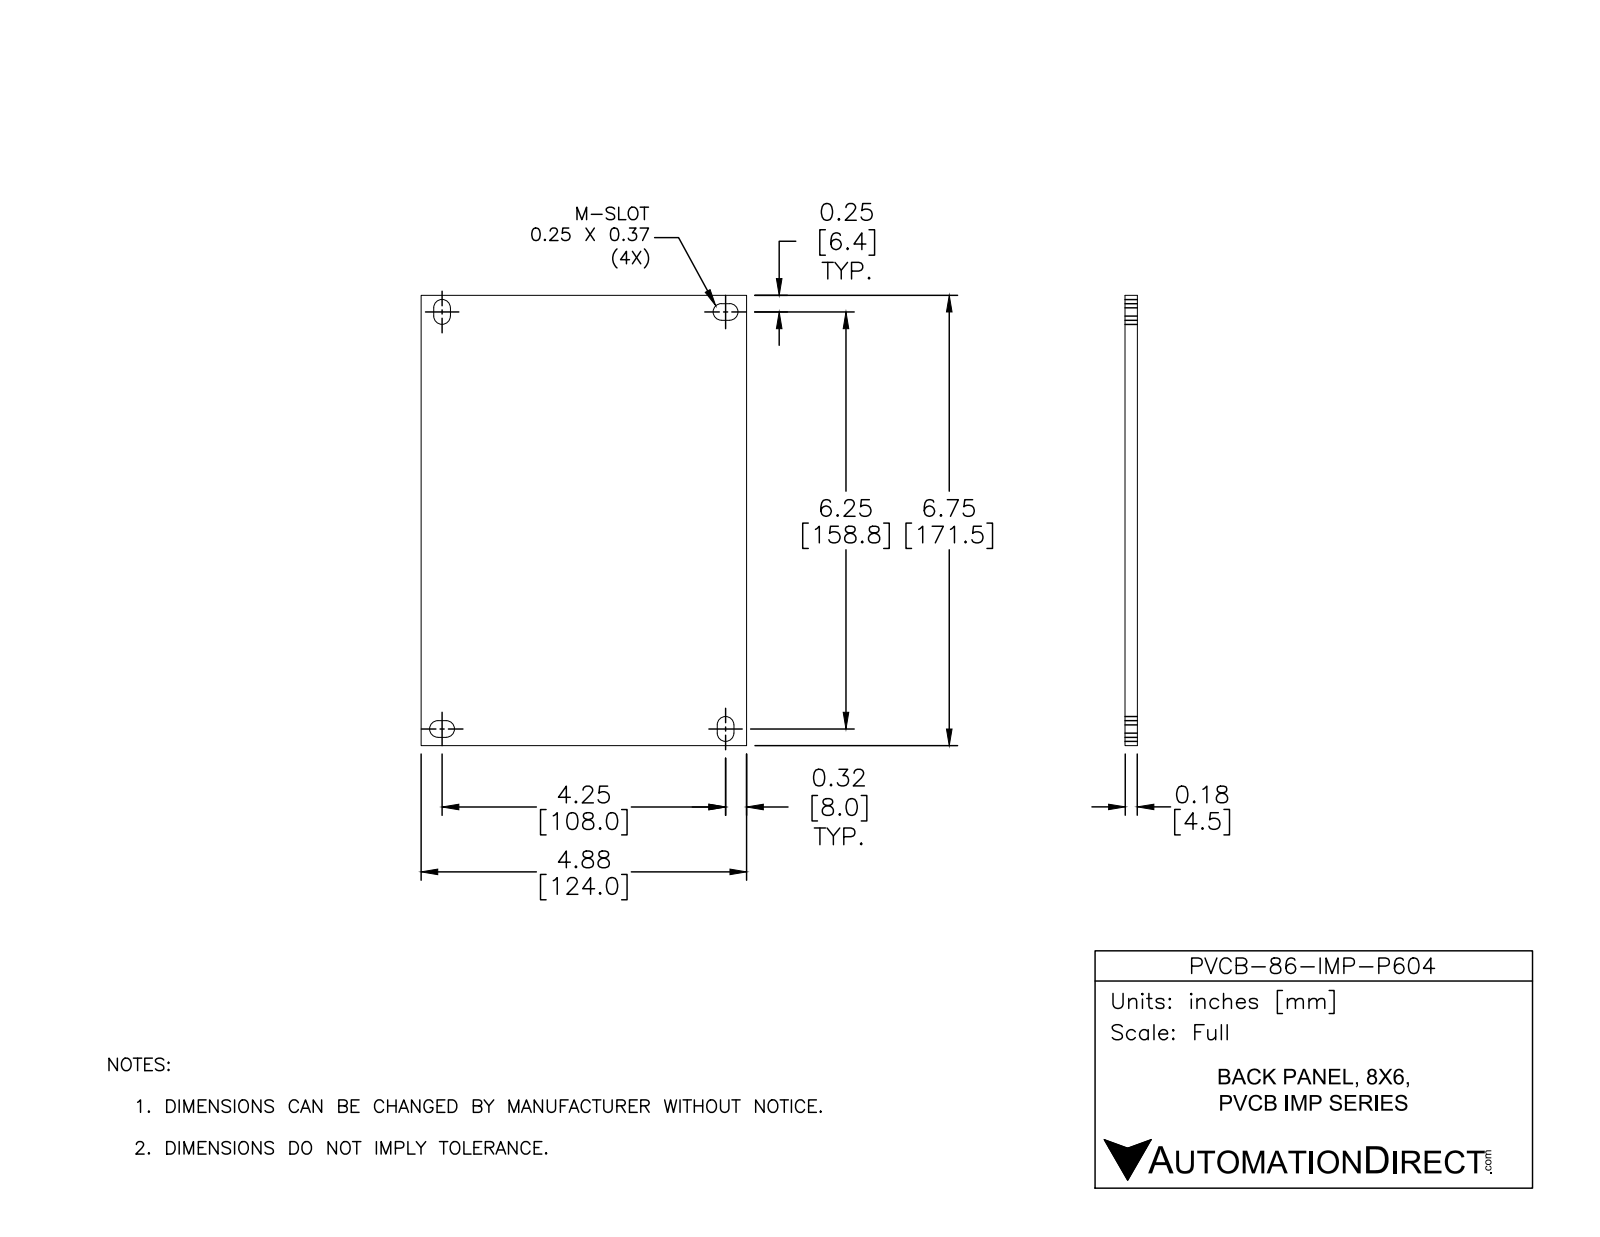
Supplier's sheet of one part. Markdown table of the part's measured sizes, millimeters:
| quantity | value |
| --- | --- |
| part name | PVCBP-86-IMP-P604 |
| STEP written by | SolidWorks 2016 (AUTOMOTIVE_DESIGN) |
| units | millimeters |
| bodies | 1 solid, 24 faces (14 planar, 10 cylindrical, 0 other) |
| overall size | 171.5 × 124 × 1.6 |
| volume | 34 270 mm³ |
| surface area | 43 230 mm² |
| partial cylindrical surfaces (radius × count) | 3.2 × 8 |
| main face-to-face distances | 1.6, 124, 171.5, 6.4, 3.2, 168.3, 108, 9.5, 161.9, 161.9 |
